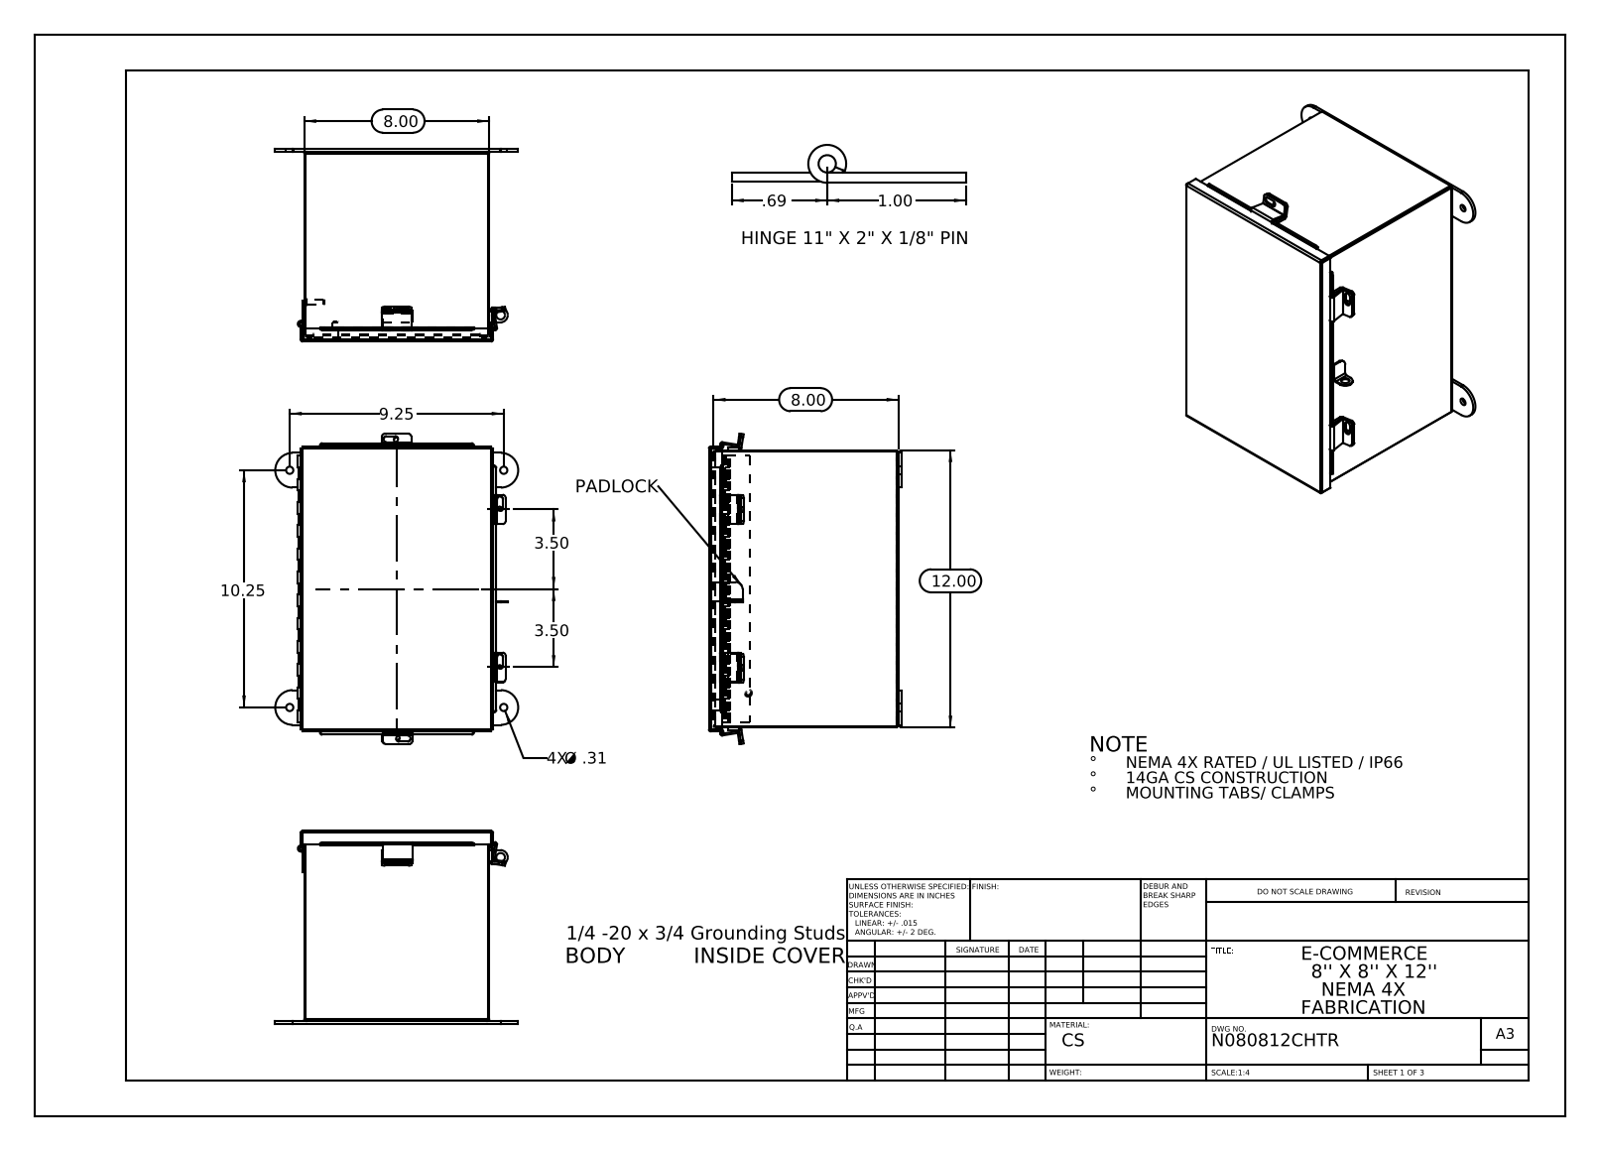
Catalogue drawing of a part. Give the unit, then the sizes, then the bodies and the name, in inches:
Units: inches
Overall size (bounding box): 13.407 × 10.5 × 8.337
Round holes (diameter × count): ⌀0.25 ×8, ⌀0.187 ×4, ⌀0.313 ×4, ⌀0.125 ×1, ⌀0.125 ×1
Round bosses / shafts (diameter × count): ⌀0.313 ×4, ⌀0.315 ×2, ⌀0.236 ×2, ⌀0.273 ×1, ⌀0.25 ×1
Partial cylindrical surfaces — rounded edges, fillets, slot ends (radius × count): R0.125 ×14, R0.009 ×12, R0.013 ×10, R0.088 ×10, R0.133 ×8, R0.083 ×6, R0.1 ×6, R0.75 ×4
Main face-to-face distances: 0.075, 7.925, 8.128, 11.925, 7.85, 8, 8.203, 8.053, 0.5, 0.074
Hole centre spacings: 10.289, 1.439, 1.439, 6.375, 7.813, 7.813, 9.25, 10.126
Volume: 52.95 in³ · Surface area: 1 401 in²
Bodies: 23 solids, 646 faces (398 planar, 228 cylindrical, 20 other)
Part name (STEP PRODUCT): N080812SSCHTR; N080812SSCHTR Hinge Cover Side JIC; N080812SSCHTR JIC Enclosure Template; N080812SSCHTR JIC_Standoff (+8 more)
STEP written by: SolidWorks 2013 (CONFIG_CONTROL_DESIGN)
